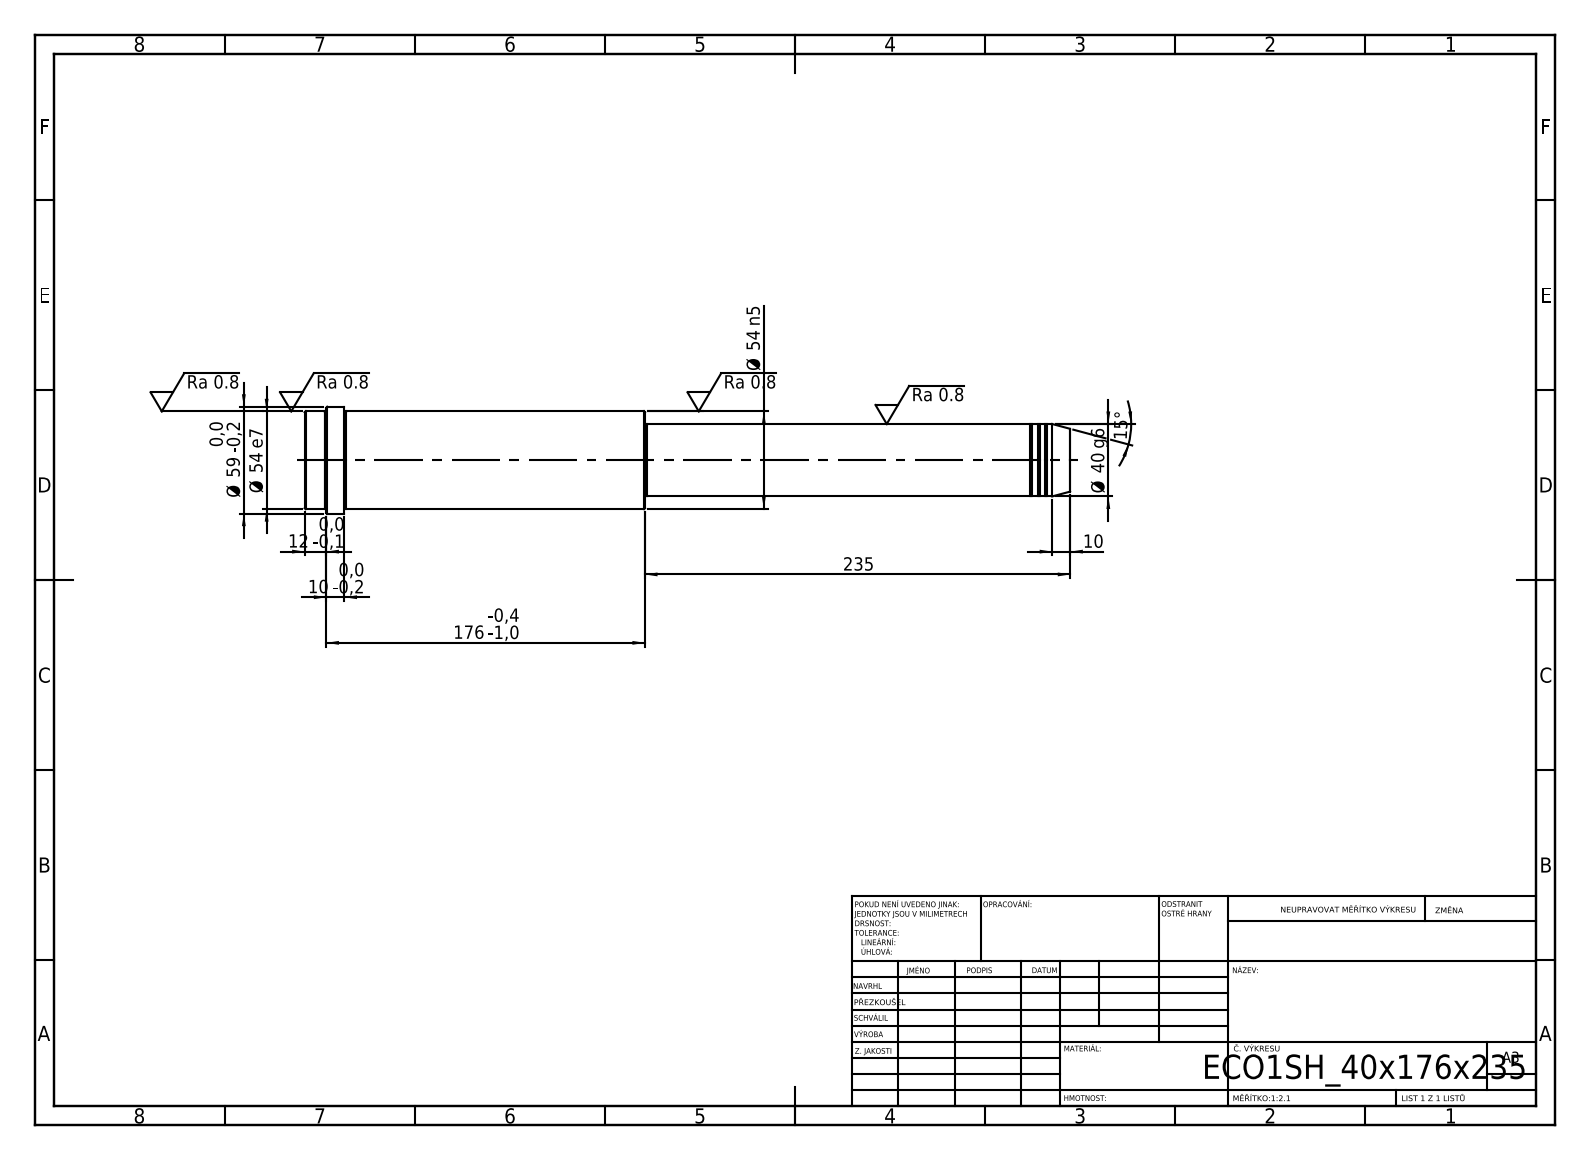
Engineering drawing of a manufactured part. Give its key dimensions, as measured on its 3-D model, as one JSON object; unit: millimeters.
{"step_written_by": "SolidWorks 2019 (CONFIG_CONTROL_DESIGN)", "units": "millimeters", "bodies": {"solids": 1, "faces": 52, "planar": 6, "cylindrical": 16, "other": 30}, "overall_size": [423, 59, 59], "volume_mm3": 728291, "surface_area_mm2": 67040, "round_bosses_or_shafts": [[59, 1], [54, 1], [40, 1], [39, 1]], "face_to_face_distances": [188, 235, 423, 401, 166, 22, 411, 176, 10, 12]}
